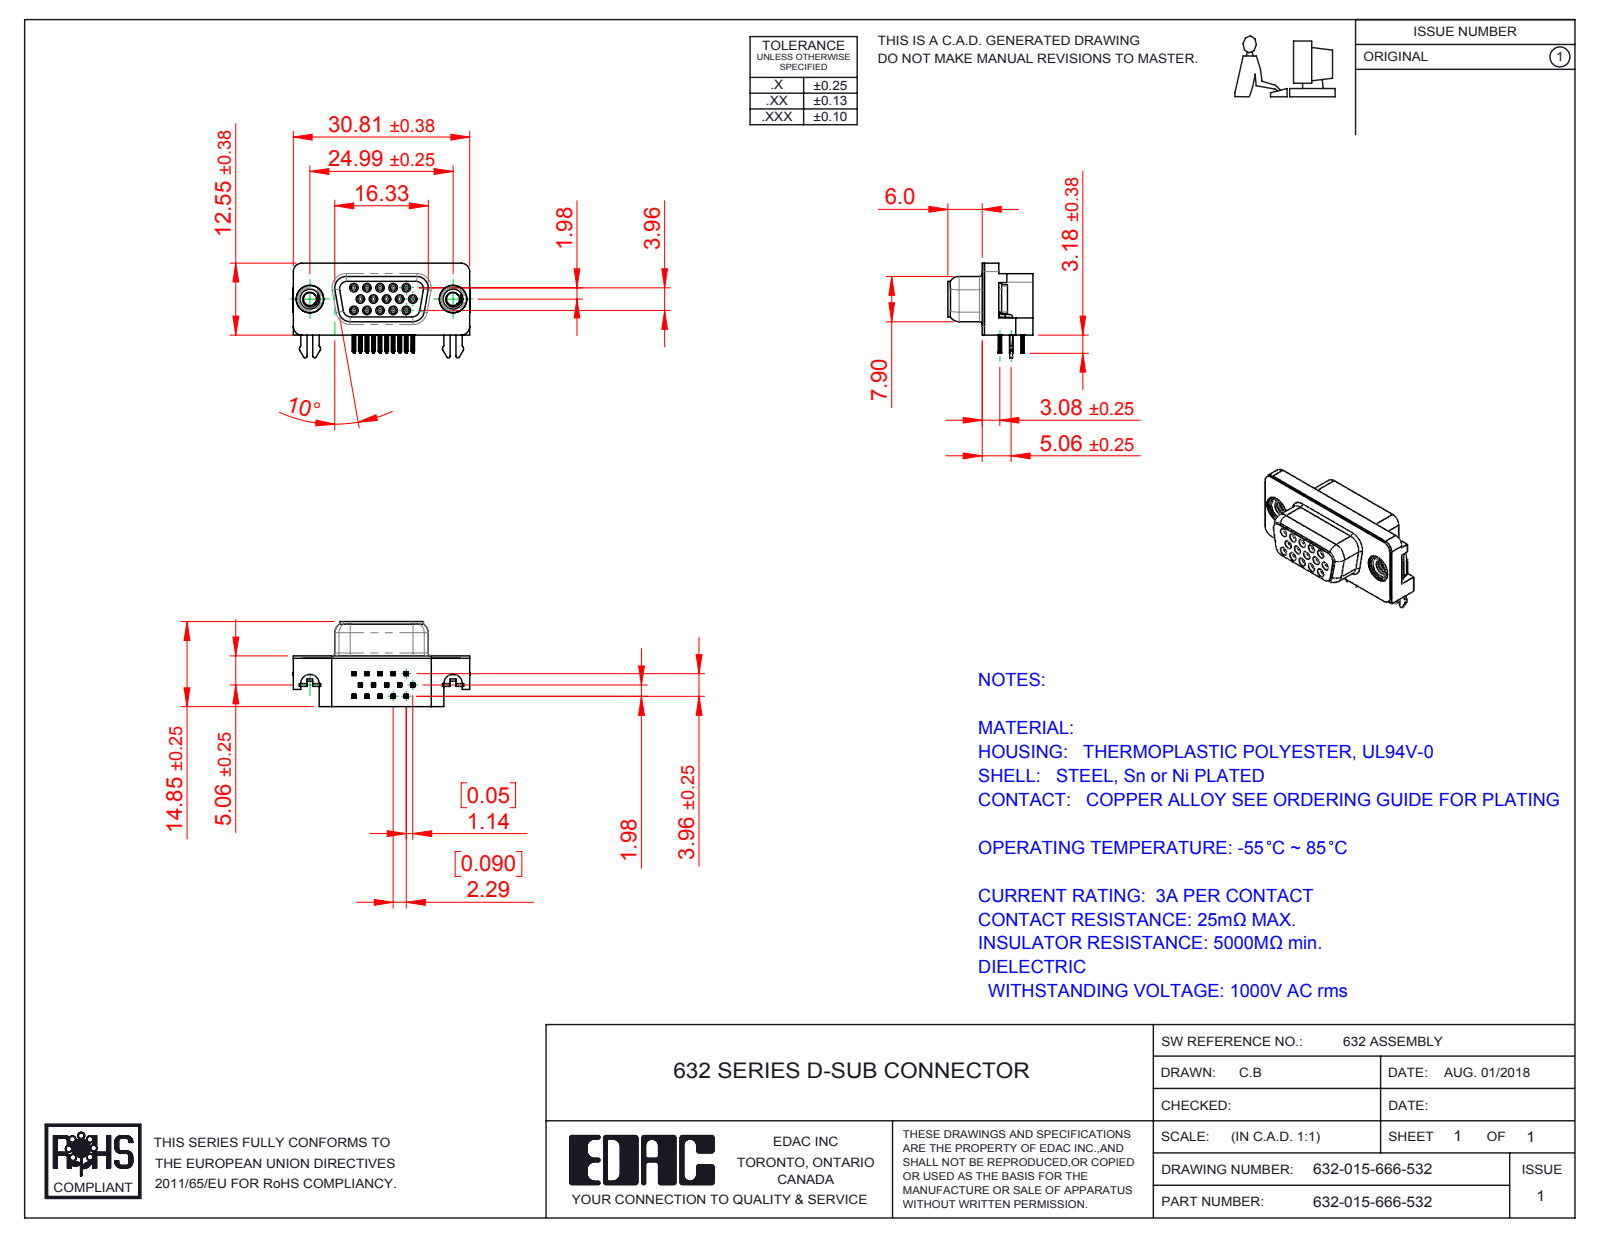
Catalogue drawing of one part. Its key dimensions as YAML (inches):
part_name: "632 Shell_9 Socket; 632 Contact Middle; 632-015-666-502; 632 4-40 Threaded Rivet (+4 more)"
step_written_by: "SolidWorks 2016 (CONFIG_CONTROL_DESIGN)"
units: inches
bodies: {solids: 21, faces: 2338, planar: 990, cylindrical: 612, other: 736}
overall_size: [1.216, 0.652, 0.585]
volume: 0.178
surface_area: 7.778
round_holes:
  - {diameter: 0.031, count: 15}
  - {diameter: 0.035, count: 15}
  - {diameter: 0.089, count: 2}
  - {diameter: 0.157, count: 2}
  - {diameter: 0.189, count: 2}
  - {diameter: 0.197, count: 2}
round_bosses_or_shafts:
  - {diameter: 0.047, count: 15}
  - {diameter: 0.193, count: 2}
  - {diameter: 0.187, count: 2}
  - {diameter: 0.154, count: 2}
partial_cylinders:
  - {radius: 0.004, count: 120}
  - {radius: 0.006, count: 60}
  - {radius: 0.014, count: 30}
  - {radius: 0.013, count: 15}
  - {radius: 0.039, count: 11}
  - {radius: 0.011, count: 10}
  - {radius: 0.02, count: 10}
  - {radius: 0.01, count: 8}
face_to_face_distances: [0.016, 0.078, 0.333, 0.348, 0.114, 0.098, 0.234, 0.252, 0.264, 0.278]
hole_center_spacings: [0.09, 0.09, 0.156, 0.18, 0.238, 0.156, 0.18, 0.27]
